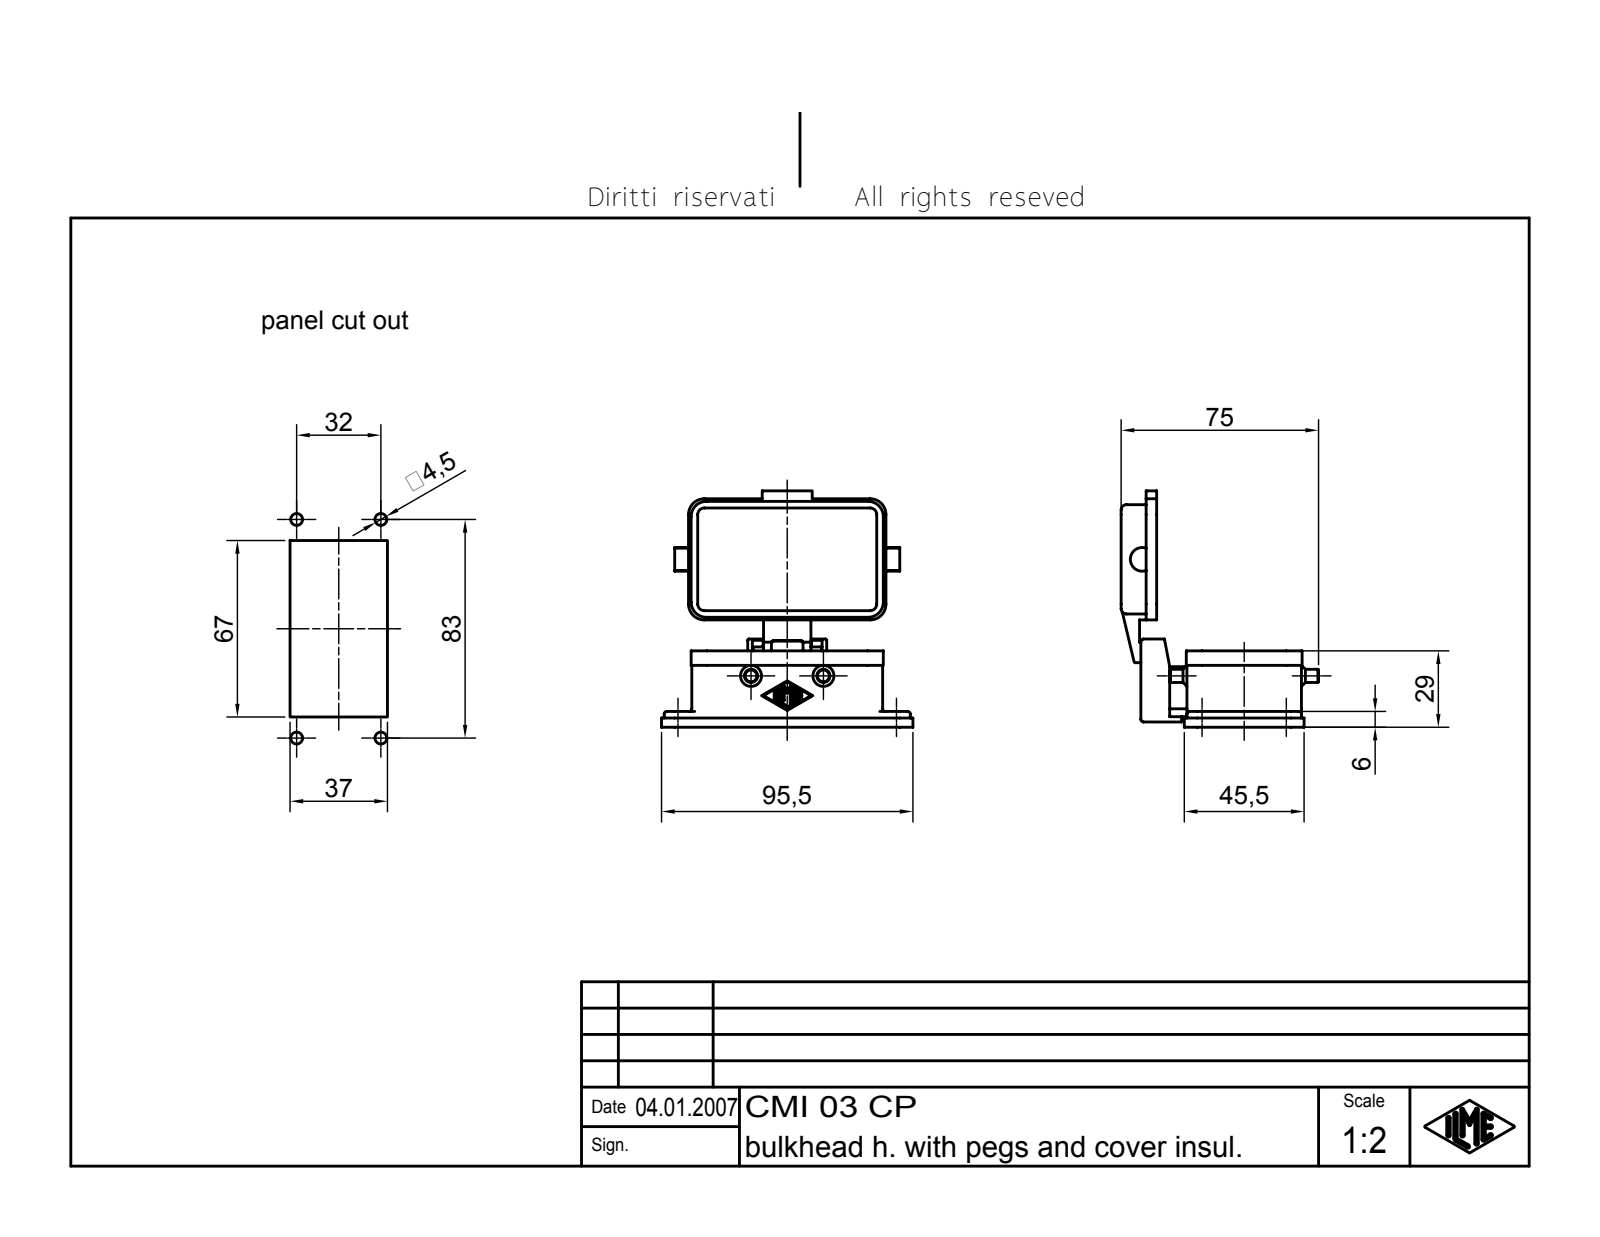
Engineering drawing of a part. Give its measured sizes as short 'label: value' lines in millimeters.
name: CMI 03 CP
written by: Autodesk Inventor 7 (AUTOMOTIVE_DESIGN)
unit: mm
bodies: 1 solid, 470 faces (205 planar, 179 cylindrical, 86 other)
size: 95.5 × 89.75 × 75
volume: 49 812 mm³; area: 36 568 mm²
holes: 4× ⌀4.5, 4× ⌀4.6, 1× ⌀4, 1× ⌀5
bosses: 2× ⌀5, 2× ⌀3, 1× ⌀7, 1× ⌀4
rounds: 14× R0.38, 12× R6, 10× R0.5, 8× R0.7, 8× R1, 8× R2, 8× R2.5, 4× R3
face distances: 2.5, 3, 4, 40.5, 0.75, 1.25, 1, 2, 40.75, 25.5
hole spacings: 32, 83, 88.96
